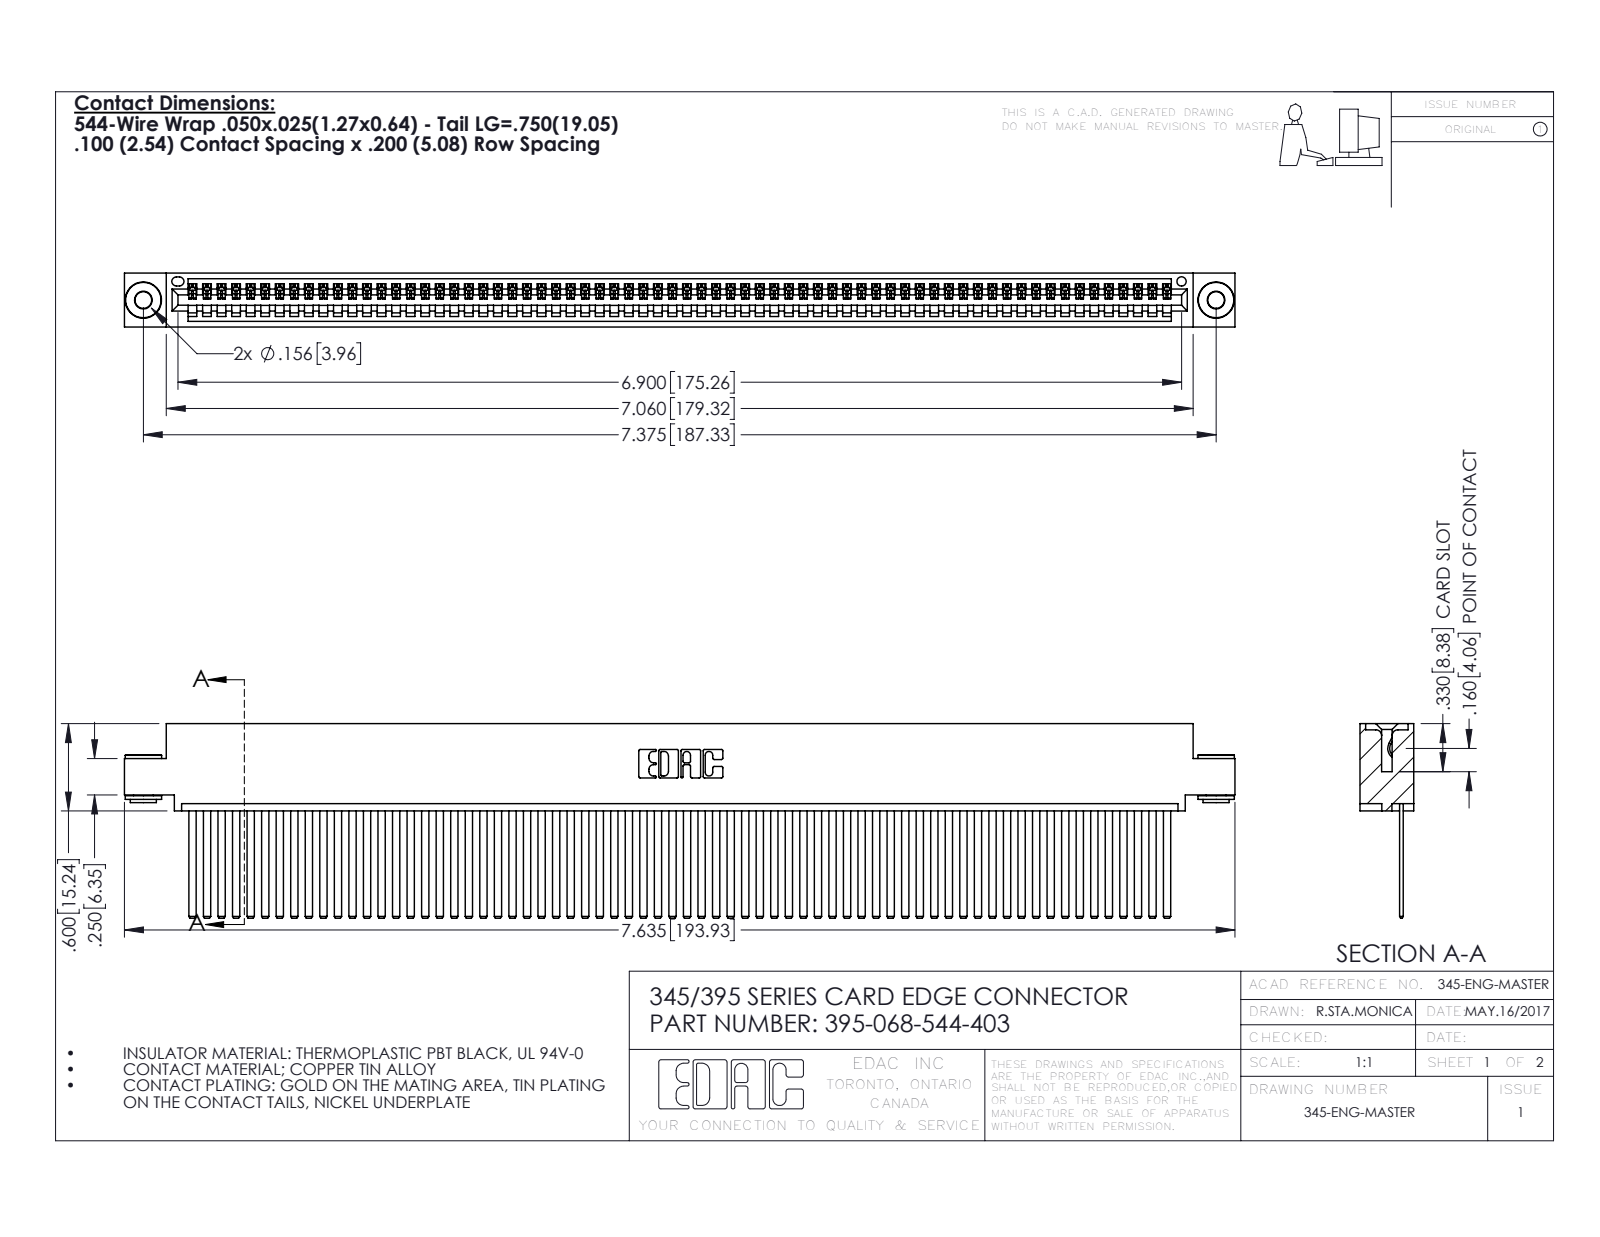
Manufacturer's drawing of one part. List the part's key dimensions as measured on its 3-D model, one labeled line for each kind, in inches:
Part name (STEP PRODUCT): 395-068-544-403; 345-292-001_345-293-144; 345-250-002_345-250-002-102; 345 Part_0.110 Offset - 0.156 Dia-TH
STEP written by: SolidWorks 2016 (CONFIG_CONTROL_DESIGN)
Units: inches
Bodies: 71 solids, 3704 faces (2542 planar, 1154 cylindrical, 8 other)
Overall size (bounding box): 7.635 × 1.337 × 0.37
Volume: 1.182 in³ · Surface area: 44.56 in²
Round holes (diameter × count): ⌀0.116 ×2, ⌀0.156 ×2, ⌀0.064 ×1
Round bosses / shafts (diameter × count): ⌀0.25 ×2, ⌀0.18 ×2, ⌀0.136 ×2
Partial cylindrical surfaces — rounded edges, fillets, slot ends (radius × count): R0.006 ×136, R0.01 ×22, R0.007 ×6, R0.031 ×6, R0.026 ×3, R0.031 ×2, R0.04 ×2, R0.014 ×1
Main face-to-face distances: 0.072, 0.298, 0.025, 0.098, 0.272, 0.37, 0.2, 0.225, 0.149, 0.072
Hole centre spacings: 0.27, 7.139, 7.375
